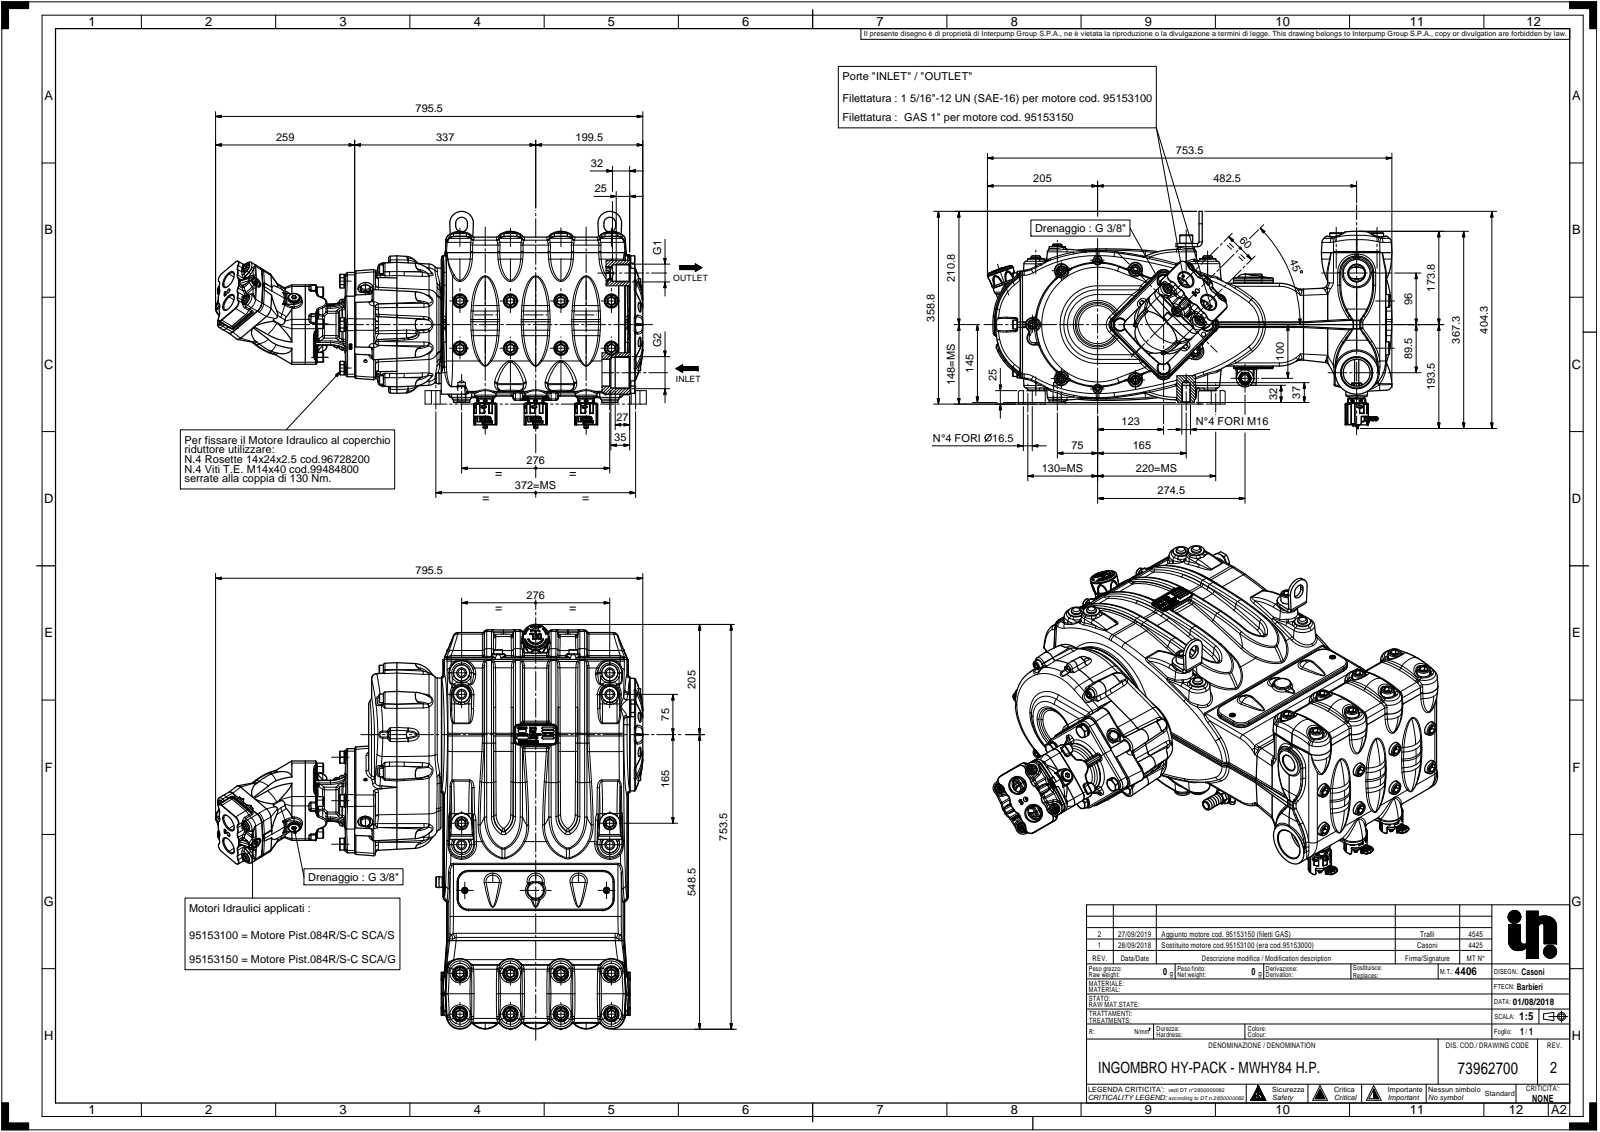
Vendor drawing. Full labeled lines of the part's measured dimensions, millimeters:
STEP written by: THINKDESIGN (CONFIG_CONTROL_DESIGN)
Units: millimetres
Bodies: 254 solids, 17798 faces (4352 planar, 4249 cylindrical, 9197 other)
Overall size (bounding box): 795.49 × 753.38 × 404.19
Volume: 60 320 000 mm³ · Surface area: 3 183 000 mm²
Round holes (diameter × count): ⌀14 ×29, ⌀17 ×29, ⌀8.5 ×25, ⌀10.5 ×19, ⌀5 ×12, ⌀8 ×12, ⌀3 ×8, ⌀11 ×8, ⌀16.5 ×8, ⌀25 ×8, ⌀26 ×8, ⌀13 ×7
Round bosses / shafts (diameter × count): ⌀16 ×43, ⌀10 ×33, ⌀24 ×22, ⌀18 ×13, ⌀19 ×6, ⌀16.8 ×6, ⌀27 ×5, ⌀30 ×4
Partial cylindrical surfaces — rounded edges, fillets, slot ends (radius × count): R0.5 ×896, R2 ×208, R3 ×136, R0.3 ×120, R0.2 ×94, R1.5 ×90, R5 ×82, R4 ×69
Main face-to-face distances: 523.5, 0.5, 350.5, 433.5, 83.5, 350, 339.66, 57, 351, 211
Hole centre spacings: 94, 84, 55.32, 60.44, 188, 52.26, 84.01, 118.8
